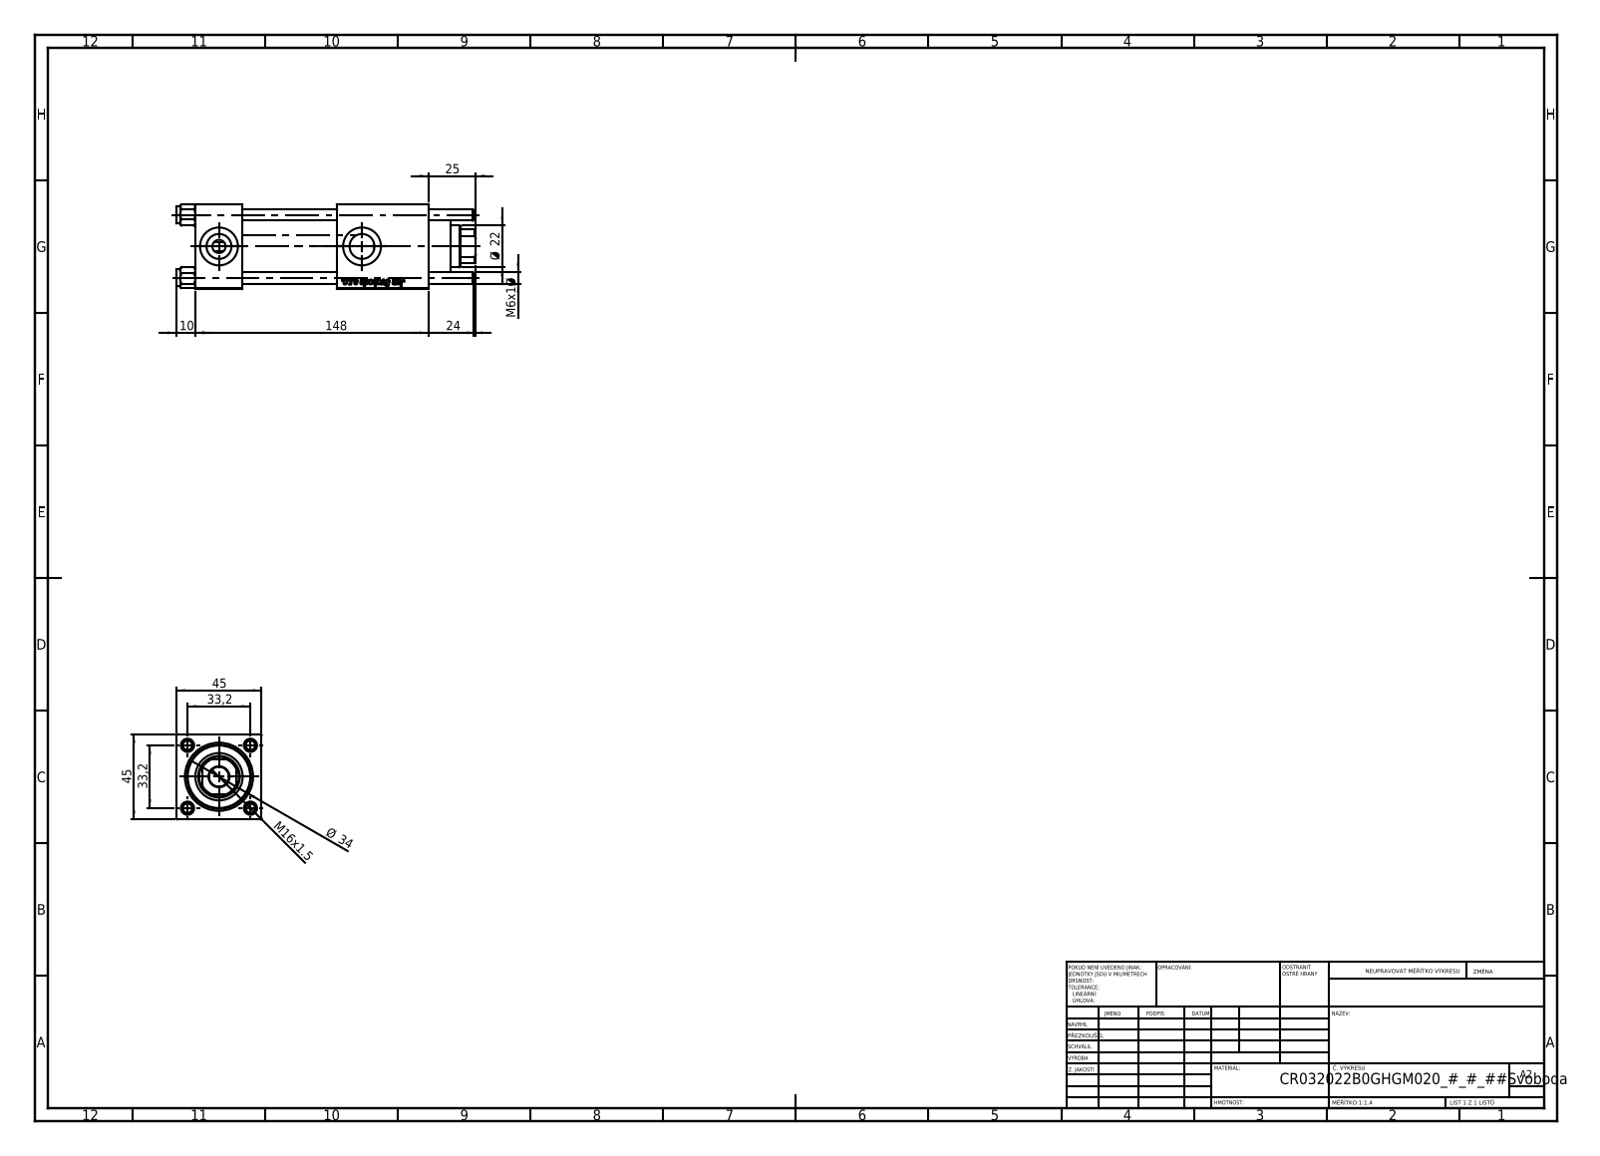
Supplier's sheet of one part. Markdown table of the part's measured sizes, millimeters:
| quantity | value |
| --- | --- |
| part name | V215_VC_A; V215CR_VCP_B; NUT_M5_B; V215CR_B_TYCINKA (+1 more) |
| STEP written by | SolidWorks 2019 (CONFIG_CONTROL_DESIGN) |
| units | millimeters |
| bodies | 11 solids, 1157 faces (431 planar, 78 cylindrical, 648 other) |
| overall size | 158 × 45 × 45 |
| volume | 214 335 mm³ |
| surface area | 76 789 mm² |
| round holes (diameter × count) | 6 × 4, 7 × 2, 13.16 × 2, 20 × 2, 10.5 × 1, 22 × 1, 24 × 1, 25 × 1, 32 × 1, 33 × 1 |
| round bosses / shafts (diameter × count) | 9 × 4, 38 × 1, 34 × 1 |
| partial cylindrical surfaces (radius × count) | 10.5 × 1 |
| main face-to-face distances | 45, 25, 50, 123, 75, 98, 48, 94.3, 69.3, 19.3 |
| hole center spacings | 23.48, 33.2, 46.95, 75.5 |
